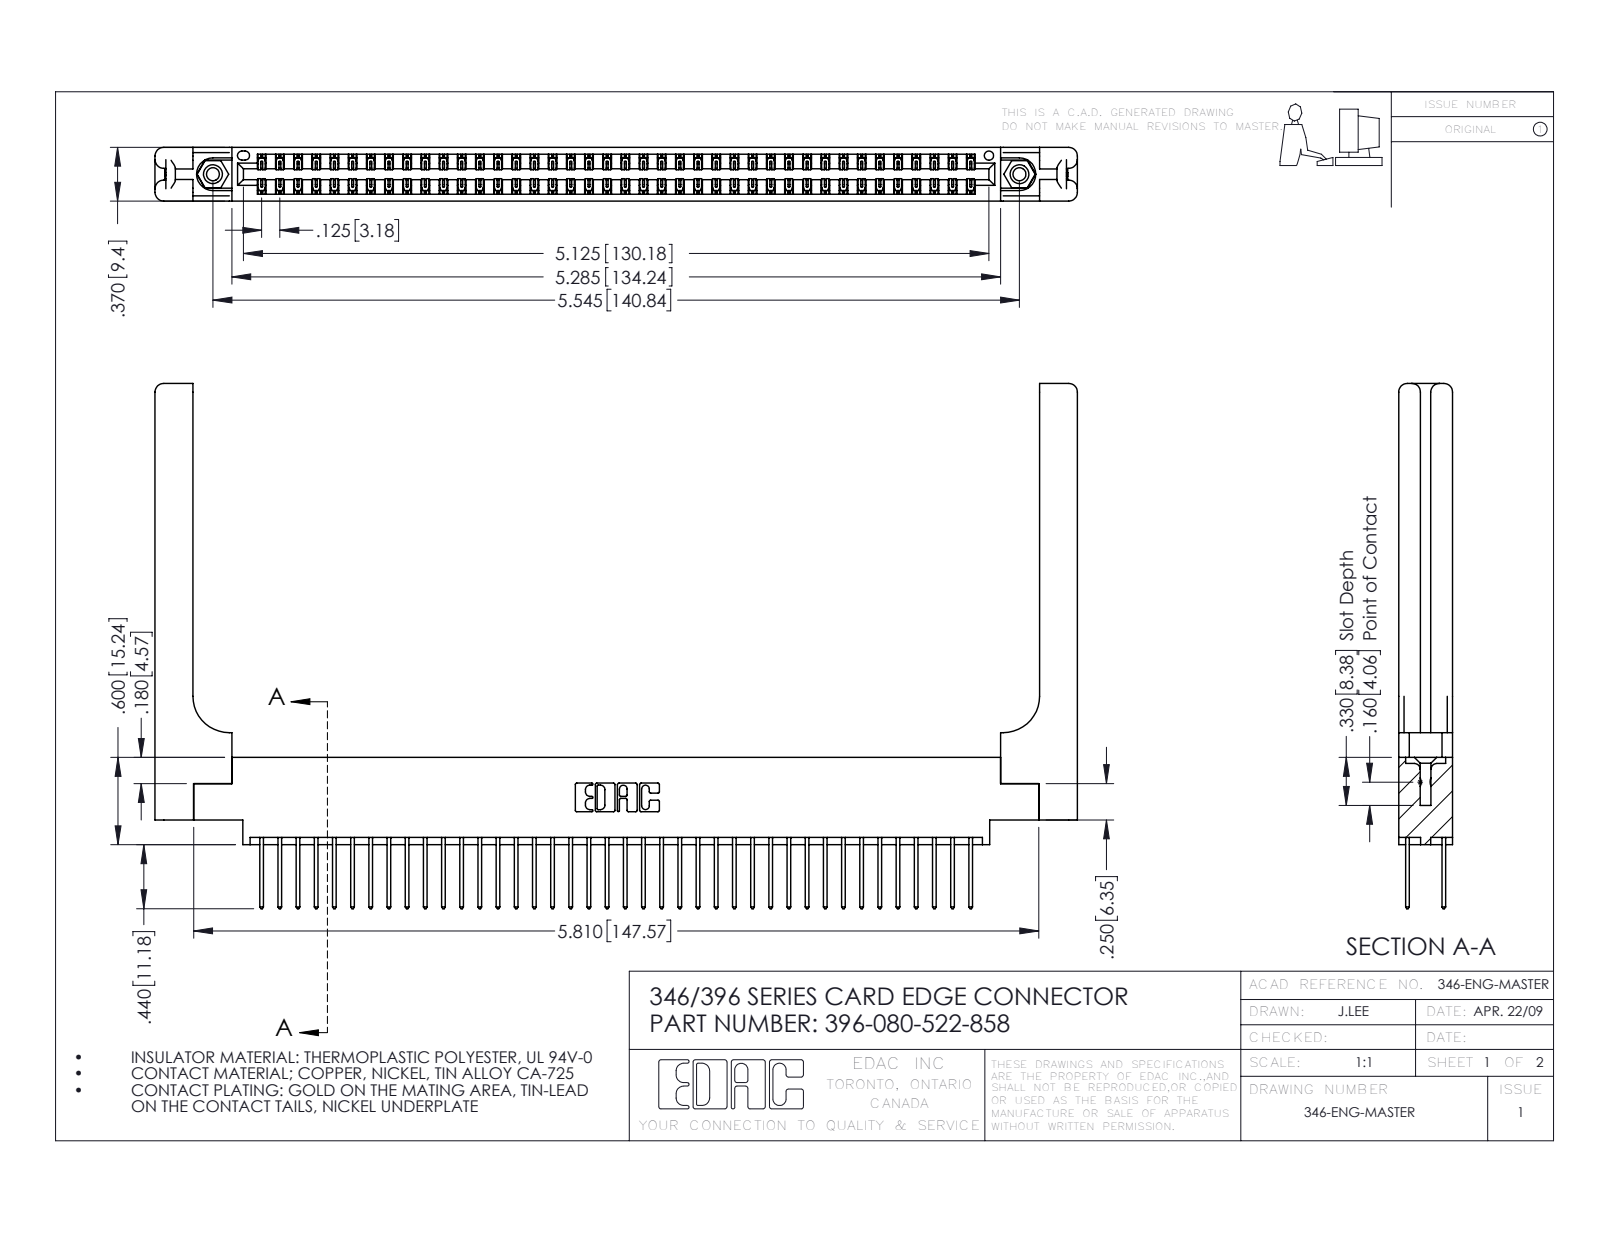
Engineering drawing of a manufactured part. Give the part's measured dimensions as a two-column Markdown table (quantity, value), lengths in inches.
| quantity | value |
| --- | --- |
| part name | 346-220-058_345-220-058; 396-080-522-858; 346 Part_0.170 Offset - 0.156 Dia-TH; 345-292-001_345-293-122 (+1 more) |
| STEP written by | SolidWorks 2016 (CONFIG_CONTROL_DESIGN) |
| units | inches |
| bodies | 85 solids, 4542 faces (3028 planar, 1454 cylindrical, 60 other) |
| overall size | 6.341 × 3.61 × 0.37 |
| volume | 1.418 in³ |
| surface area | 42.95 in² |
| round holes (diameter × count) | 0.089 × 2, 0.125 × 2, 0.156 × 2, 0.064 × 1 |
| round bosses / shafts (diameter × count) | 0.155 × 2 |
| partial cylindrical surfaces (radius × count) | 0.006 × 120, 0.01 × 80, 0.01 × 22, 0.06 × 16, 0.007 × 6, 0.031 × 6, 0.026 × 3, 0.014 × 2 |
| main face-to-face distances | 0.048, 0.322, 0.37, 0.072, 0.25, 0.025, 0.298, 0.15, 0.148, 0.275 |
| hole center spacings | 0.246, 5.336, 5.545 |
